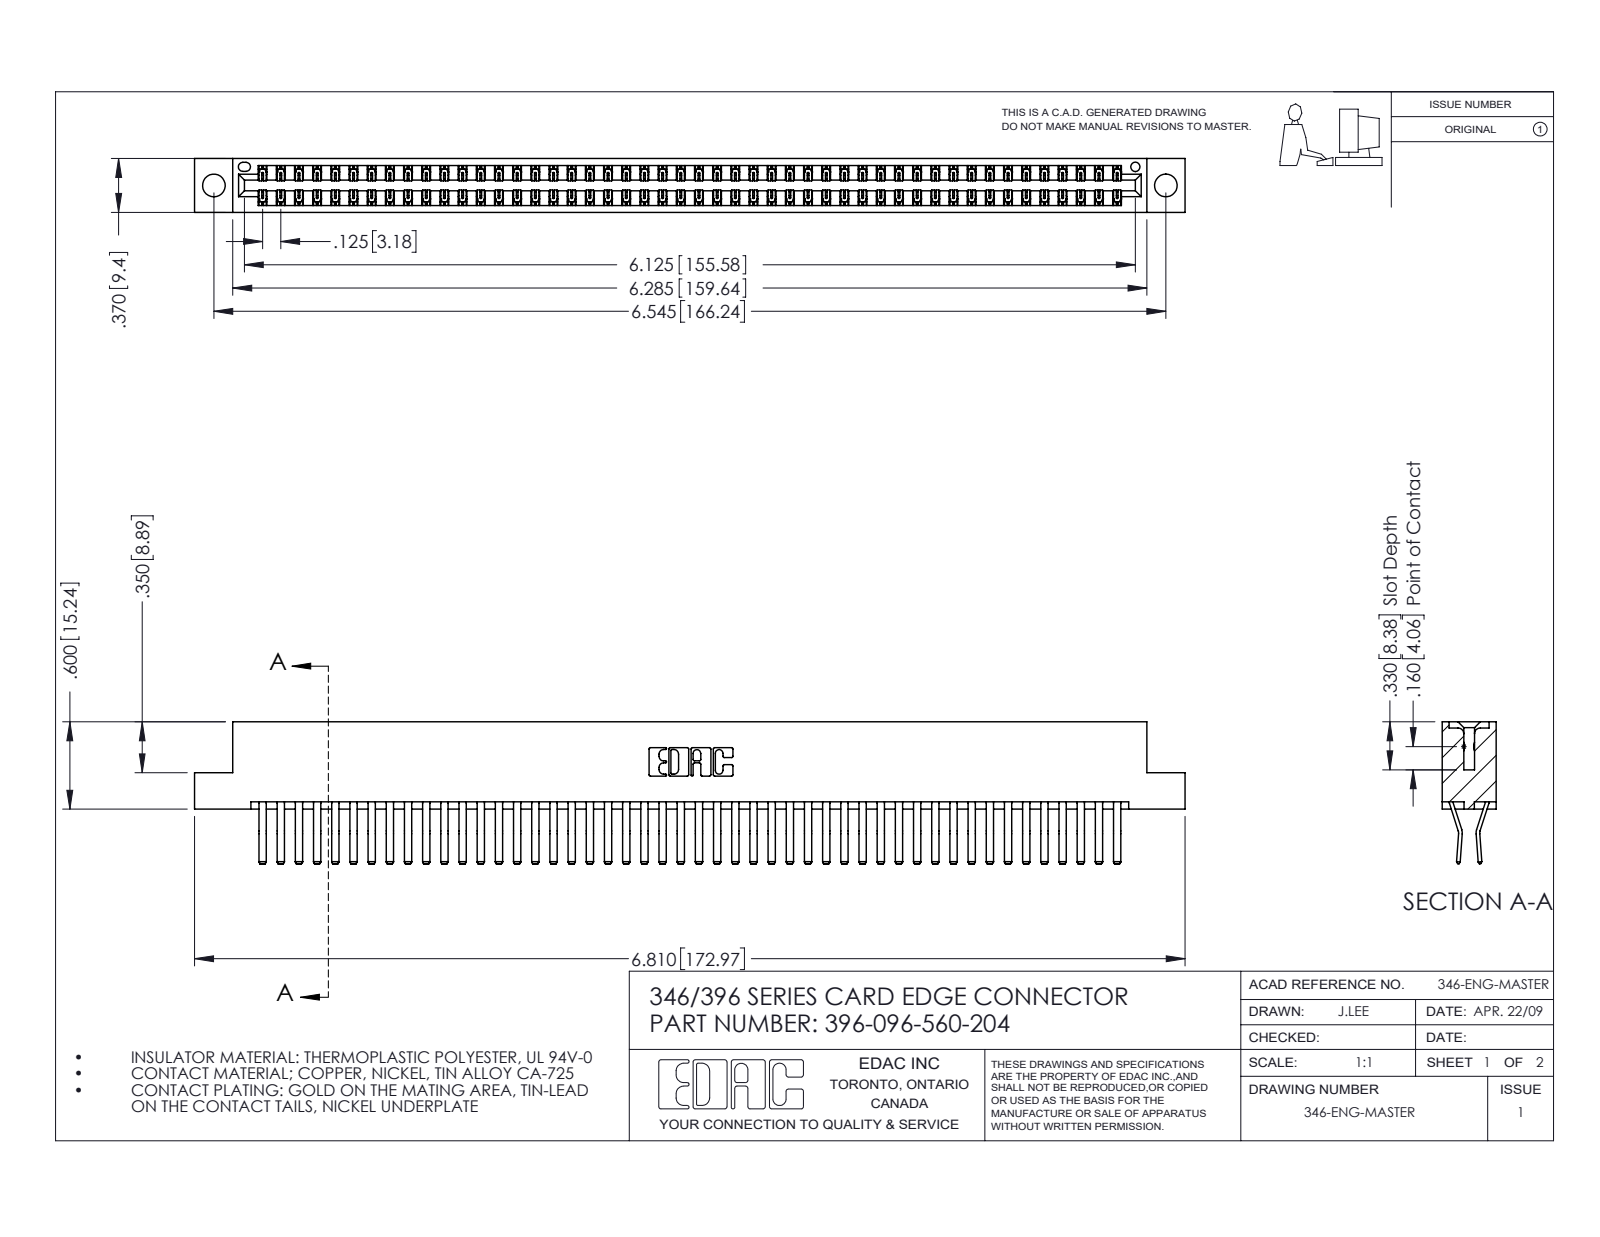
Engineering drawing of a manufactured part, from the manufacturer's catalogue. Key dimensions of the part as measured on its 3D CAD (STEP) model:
Part name (STEP PRODUCT): 345-292-001_560 Tail; 396-096-560-204; 346 Part_Flush Mounting Lugs - 0.156 Dia-TH
STEP written by: SolidWorks 2016 (CONFIG_CONTROL_DESIGN)
Units: inches
Bodies: 97 solids, 5306 faces (3436 planar, 1870 cylindrical, 0 other)
Overall size (bounding box): 6.81 × 0.975 × 0.37
Volume: 1.065 in³ · Surface area: 39.65 in²
Round holes (diameter × count): ⌀0.156 ×2, ⌀0.064 ×1
Partial cylindrical surfaces — rounded edges, fillets, slot ends (radius × count): R0.006 ×144, R0.01 ×22, R0.007 ×6, R0.031 ×6, R0.026 ×3, R0.01 ×2, R0.014 ×2, R0.022 ×2
Main face-to-face distances: 0.048, 0.322, 0.37, 0.025, 0.25, 0.072, 0.298, 0.275, 0.148, 0.222
Hole centre spacings: 0.246, 6.336, 6.545
